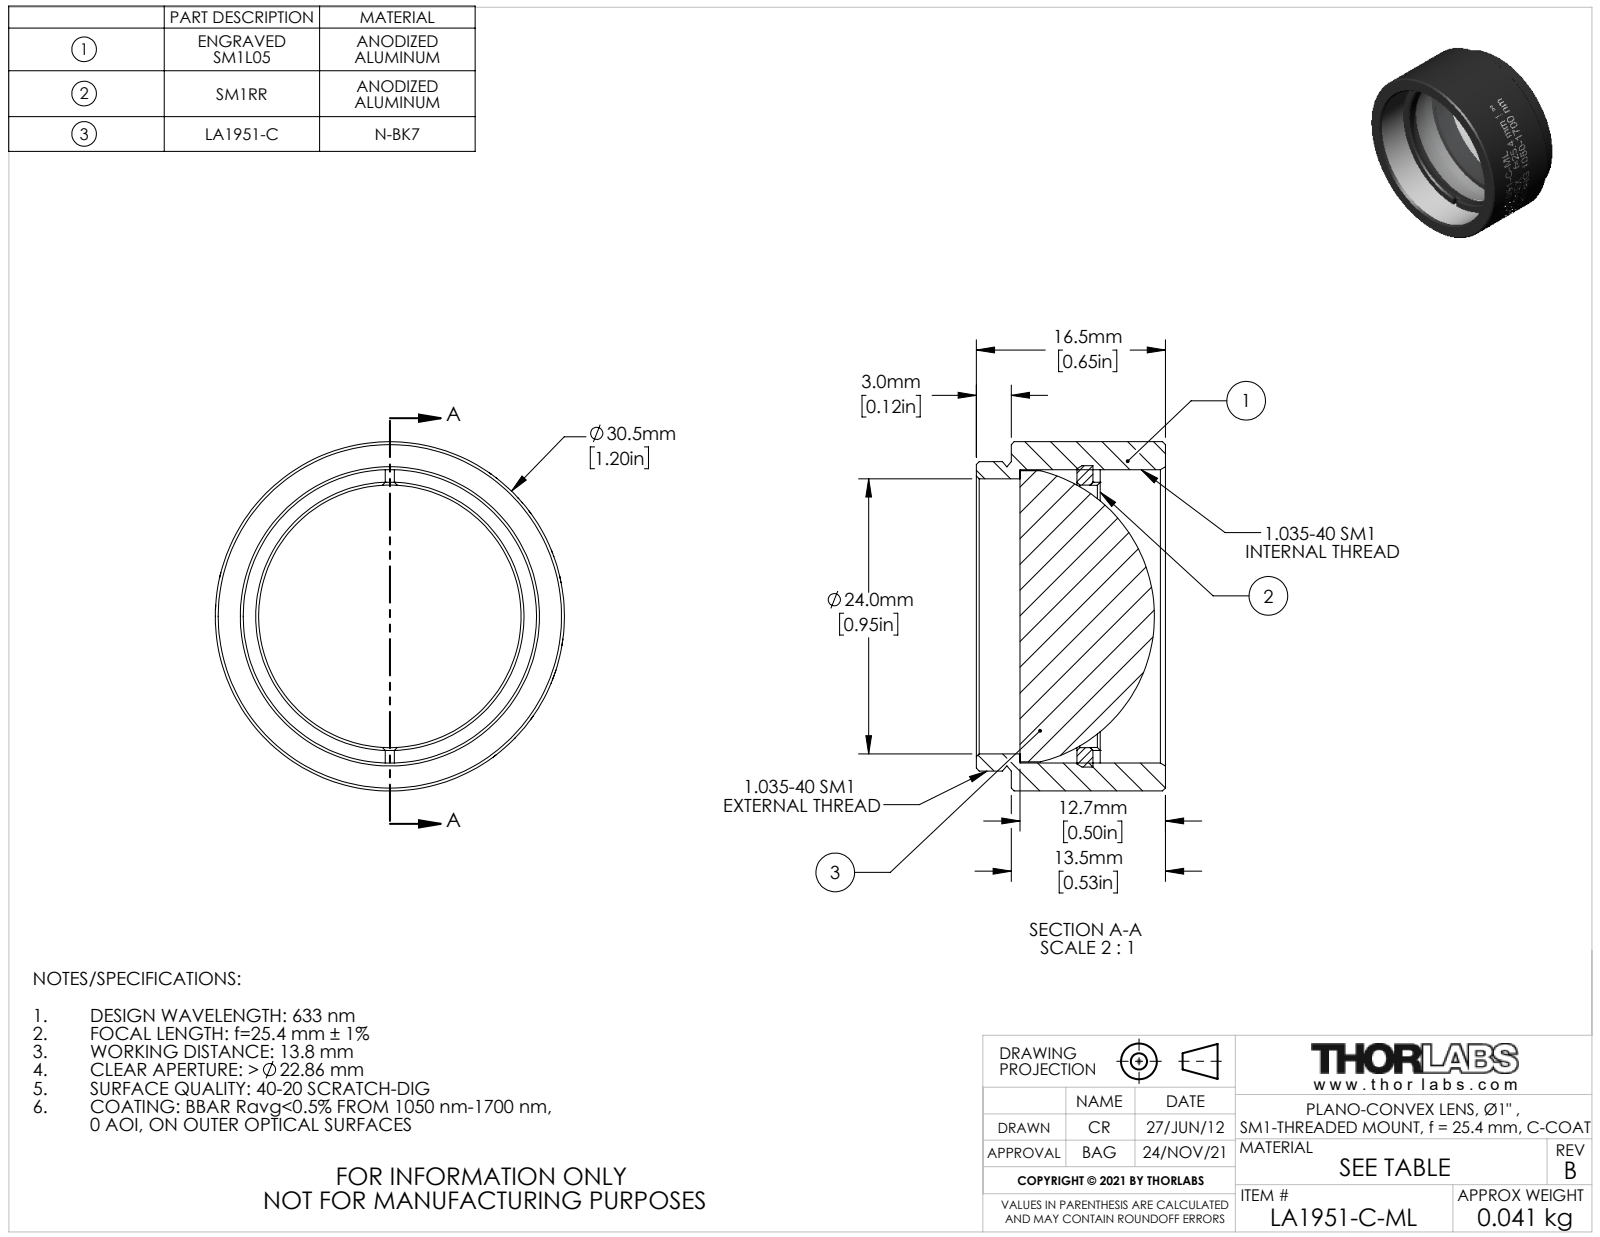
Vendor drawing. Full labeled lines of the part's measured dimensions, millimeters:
Part name (STEP PRODUCT): 24417-999
STEP written by: SolidWorks 2018 (AUTOMOTIVE_DESIGN)
Units: millimetres
Bodies: 3 solids, 873 faces (344 planar, 109 cylindrical, 420 other)
Overall size (bounding box): 30.48 × 30.48 × 16.51
Volume: 7 467 mm³ · Surface area: 5 375 mm²
Round holes (diameter × count): ⌀22.91 ×1, ⌀24 ×1, ⌀25.6 ×1
Round bosses / shafts (diameter × count): ⌀30.48 ×1, ⌀27 ×1, ⌀26.29 ×1, ⌀25.4 ×1
Partial cylindrical surfaces — rounded edges, fillets, slot ends (radius × count): R15.23 ×1
Main face-to-face distances: 12.7, 0.77, 13.47, 5.74, 4.97, 7.73, 2.03, 7.77, 7, 5.7
